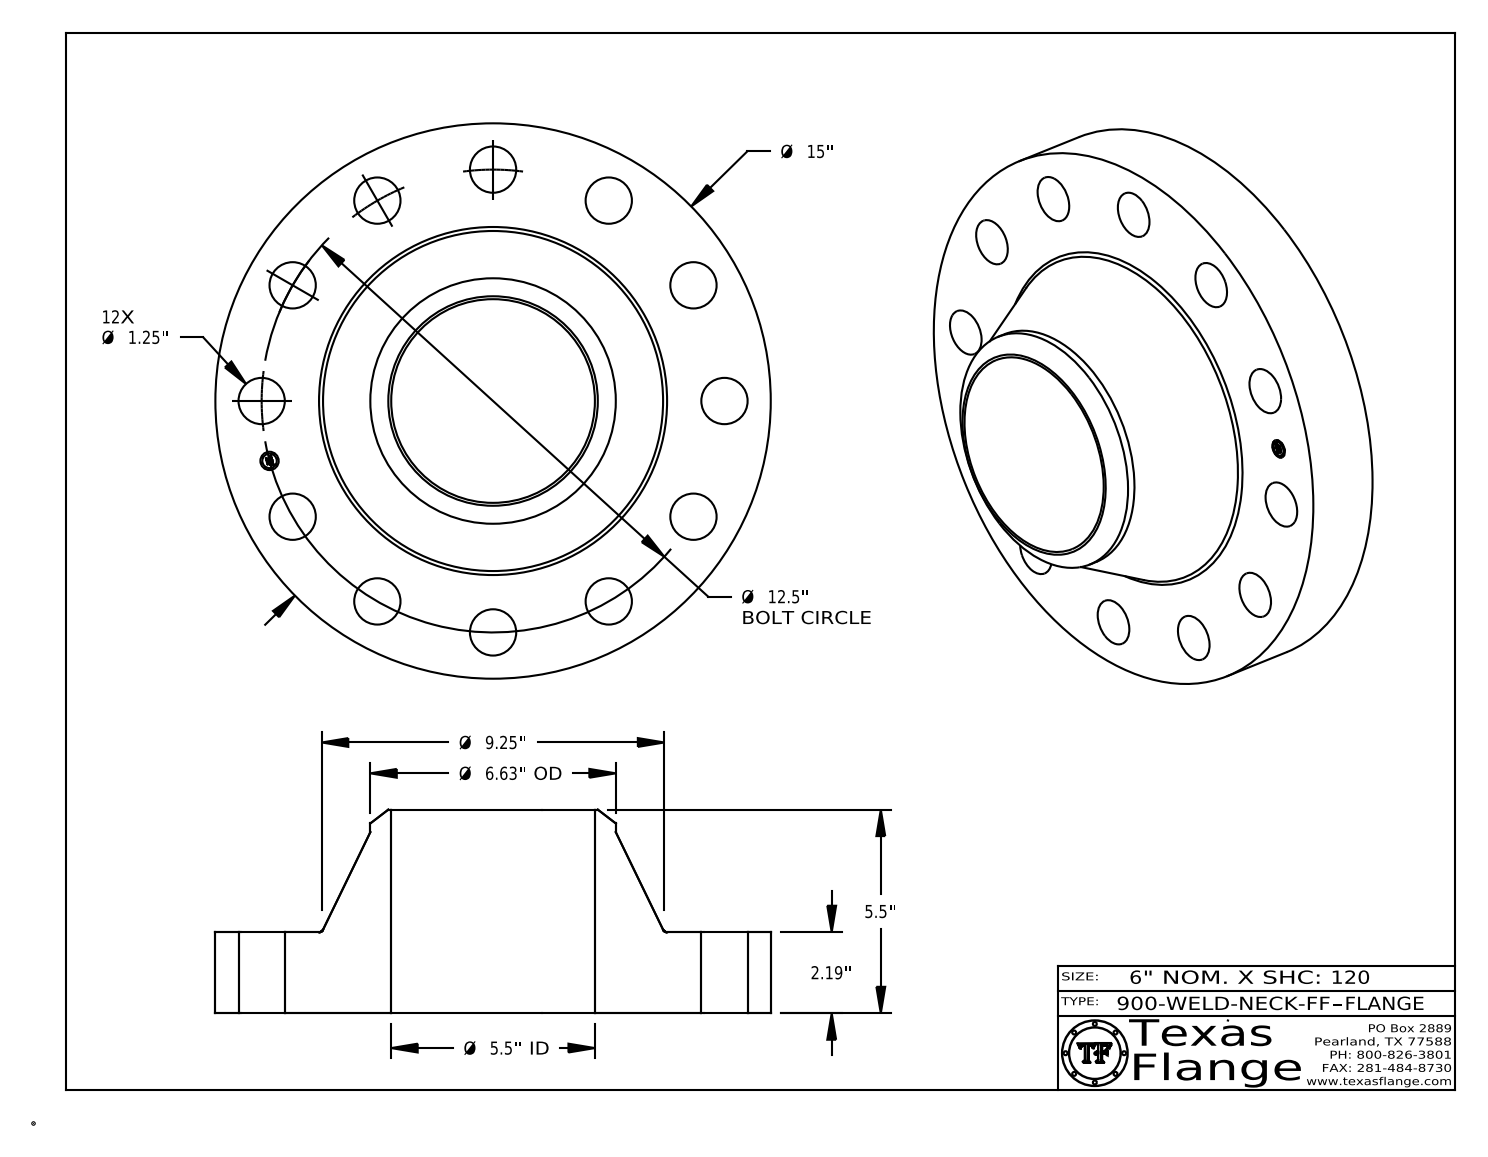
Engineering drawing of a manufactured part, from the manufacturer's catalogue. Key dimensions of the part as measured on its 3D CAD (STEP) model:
Part name (STEP PRODUCT): 900-WELD-NECK-FF
STEP written by: CATIA V5 STEP AP214 (AUTOMOTIVE_DESIGN)
Units: inches
Bodies: 1 solid, 424 faces (368 planar, 50 cylindrical, 6 other)
Overall size (bounding box): 15 × 15 × 5.5
Volume: 378.2 in³ · Surface area: 627.1 in²
Round holes (diameter × count): ⌀1.25 ×12, ⌀0.495 ×1, ⌀5.501 ×1
Round bosses / shafts (diameter × count): ⌀0.03 ×8, ⌀15 ×1, ⌀6.63 ×1, ⌀0.39 ×1
Main face-to-face distances: 2.19, 5.5, 3.31, 2.175, 0.015, 3.325, 0.148, 0.144, 0.027, 0.096
Hole centre spacings: 6.25, 8.839, 3.235, 10.826, 12.074, 12.5, 3.235, 6.25
